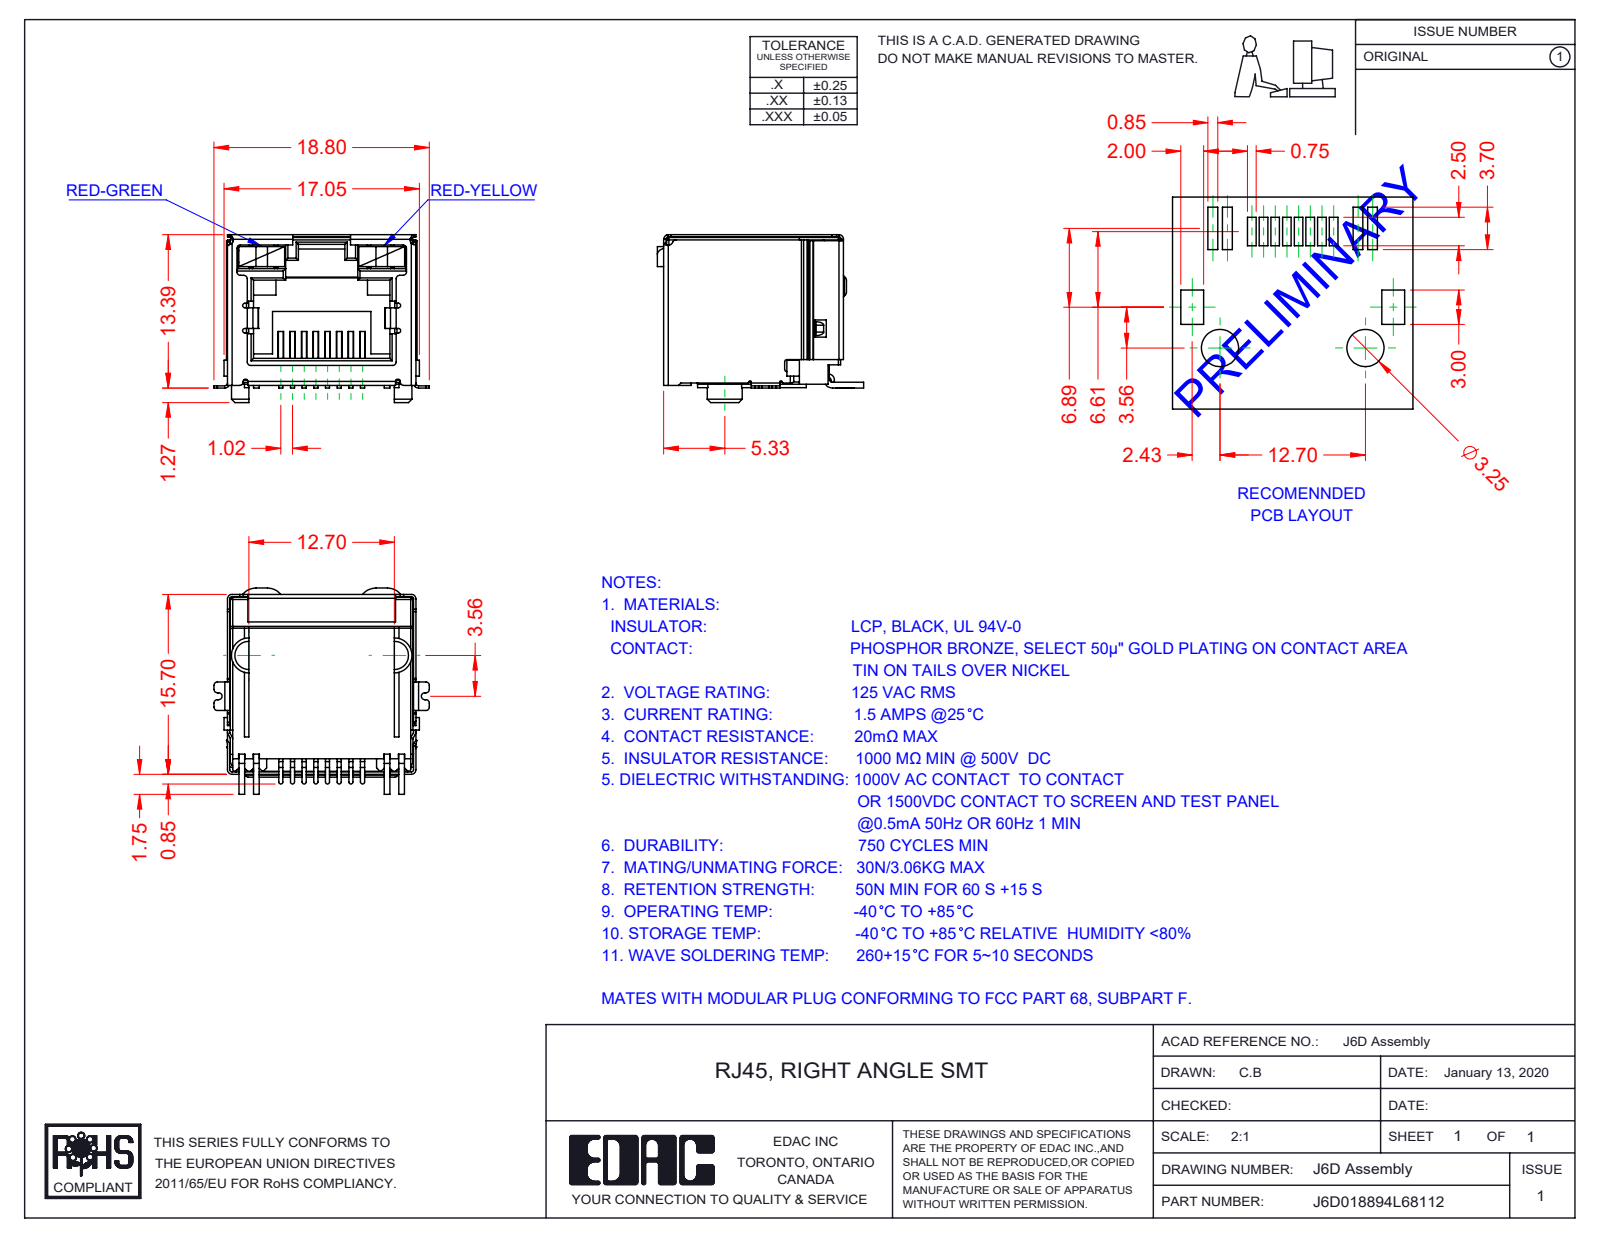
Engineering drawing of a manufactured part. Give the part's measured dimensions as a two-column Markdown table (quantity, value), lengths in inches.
| quantity | value |
| --- | --- |
| part name | 6D Shield_LED - No EMI; 6D Insulator; J6D018894L68112; 6D LED LH_6-Red-Green (+2 more) |
| STEP written by | SolidWorks 2016 (CONFIG_CONTROL_DESIGN) |
| units | inches |
| bodies | 12 solids, 899 faces (646 planar, 220 cylindrical, 33 other) |
| overall size | 0.74 × 0.709 × 0.577 |
| volume | 0.11 in³ |
| surface area | 7.592 in² |
| partial cylindrical surfaces (radius × count) | 0.012 × 39, 0.008 × 37, 0.016 × 16, 0.004 × 12, 0.006 × 8, 0.007 × 8, 0.02 × 6, 0.059 × 5 |
| main face-to-face distances | 0.63, 0.64, 0.638, 0.089, 0.039, 0.628, 0.632, 0.504, 0.018, 0.648 |
